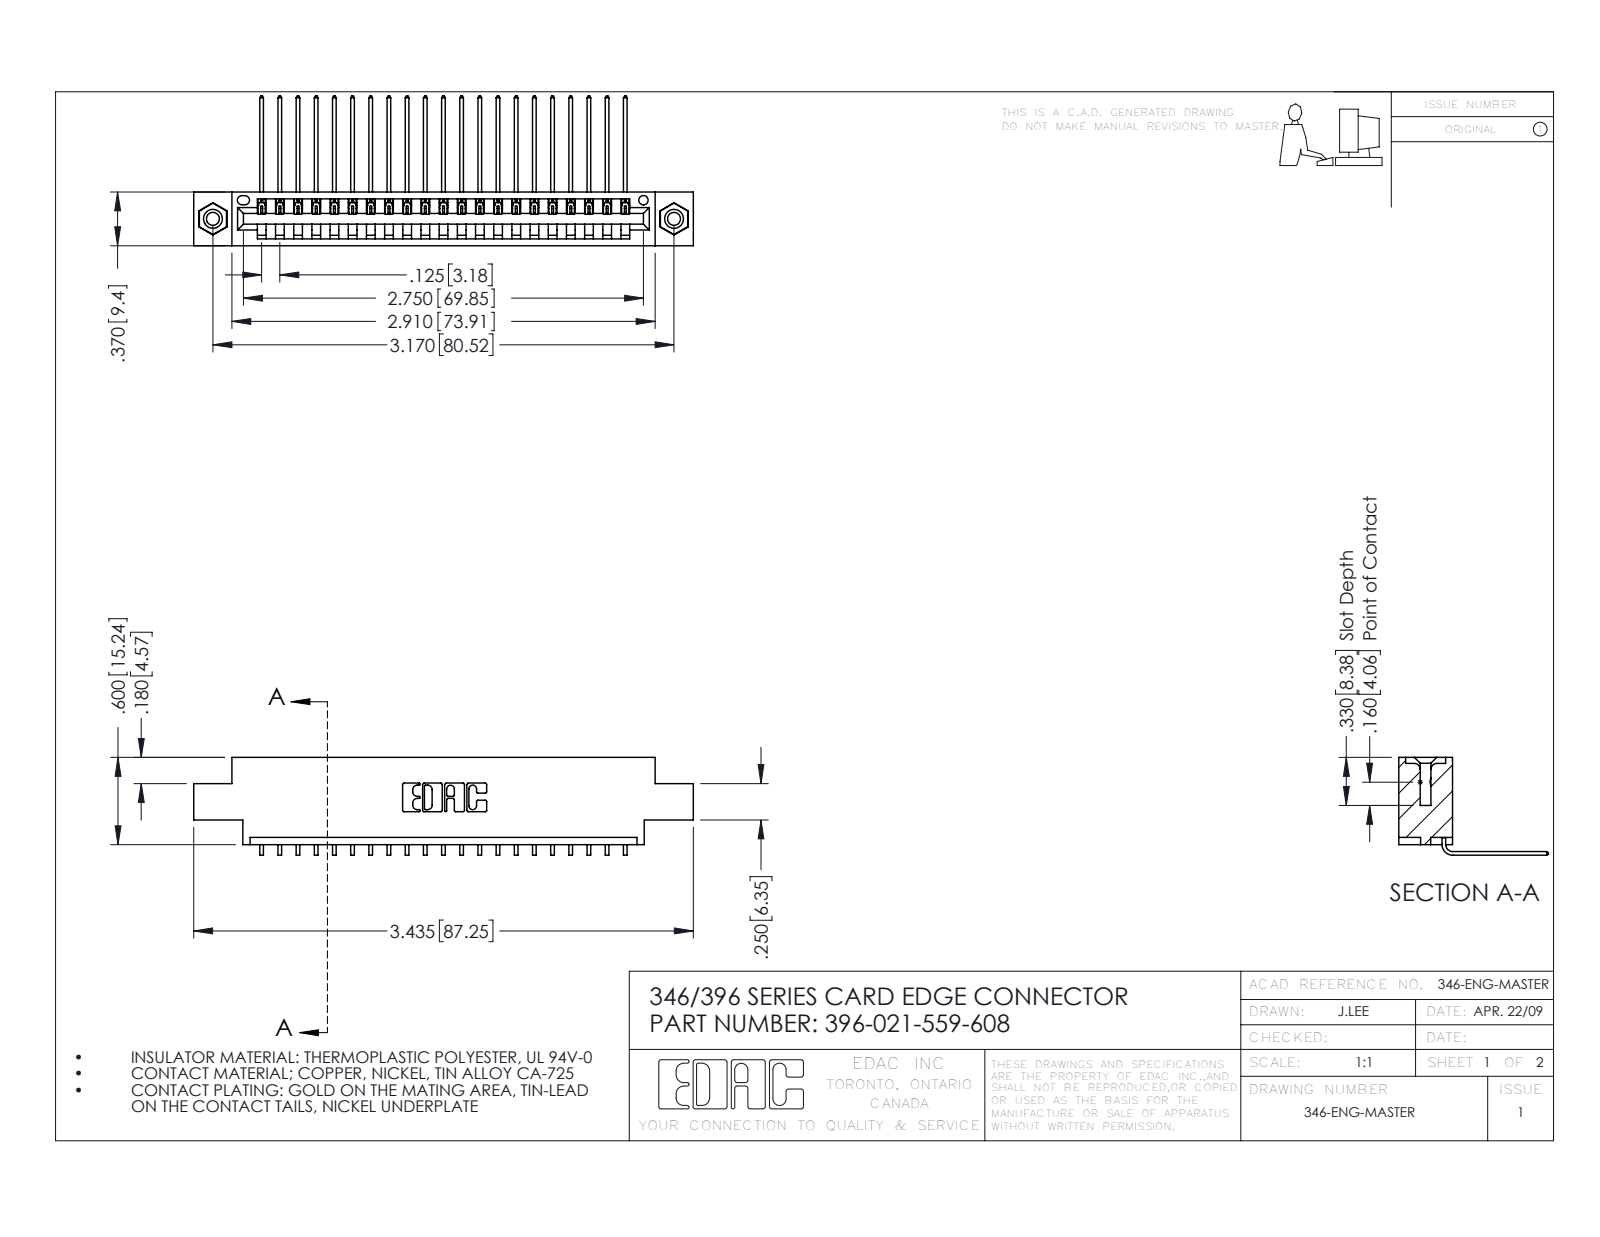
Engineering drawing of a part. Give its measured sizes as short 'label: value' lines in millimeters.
name: 346 Part_0.170 Offset - 0.156 Dia-TI; 396-021-559-608; 345-292-001_558 559 Tail - 1; 345-250-001_345-250-003-102
written by: SolidWorks 2016 (CONFIG_CONTROL_DESIGN)
unit: mm
bodies: 24 solids, 1446 faces (994 planar, 436 cylindrical, 16 other)
size: 87.2 × 26.2 × 17.1
volume: 8 110 mm³; area: 10 520 mm²
holes: 2× ⌀2.3, 2× ⌀3.2, 2× ⌀4, 1× ⌀1.6
bosses: 2× ⌀3.9
rounds: 42× R0.2, 22× R0.3, 6× R0.2, 6× R0.8, 3× R0.7, 2× R0.8, 2× R1, 1× R0.4
face distances: 1.2, 8.2, 9.4, 6.4, 0.6, 1.8, 5.6, 3.8, 2.5, 4.4
hole spacings: 6.2, 75.3, 80.5
